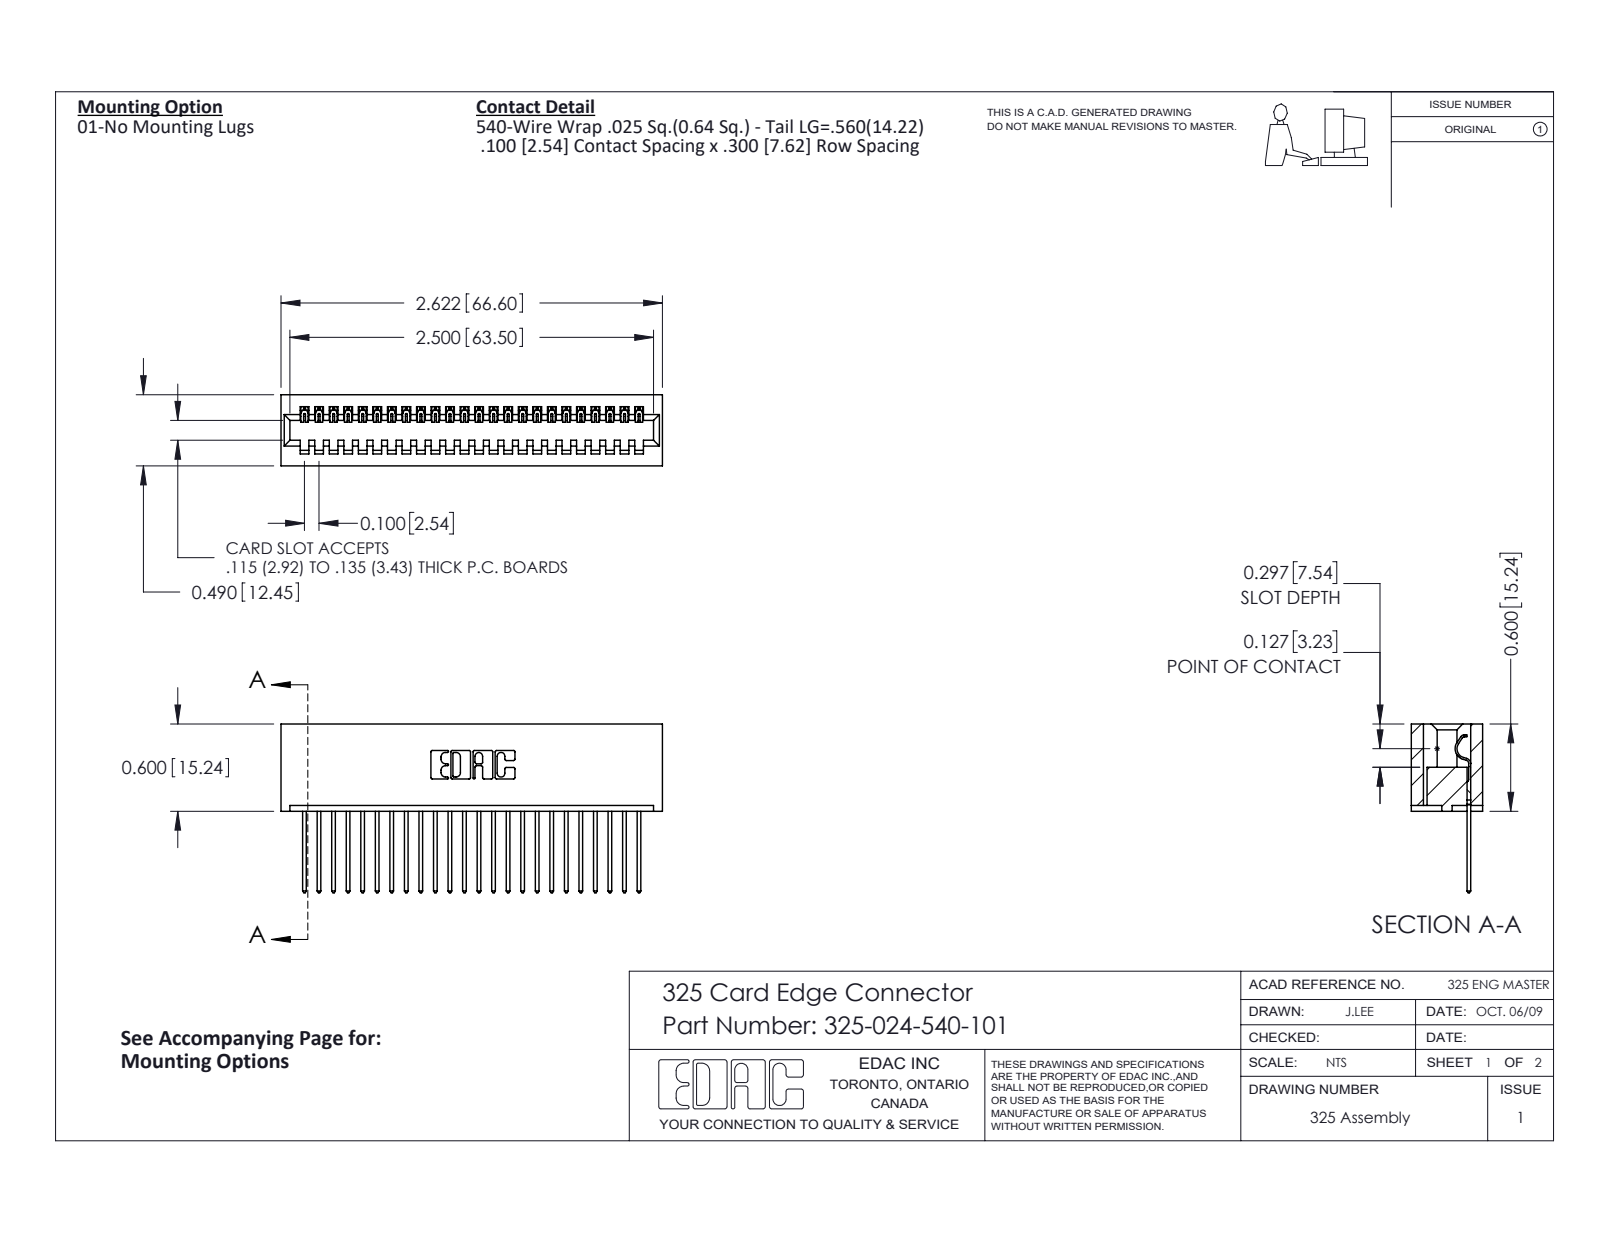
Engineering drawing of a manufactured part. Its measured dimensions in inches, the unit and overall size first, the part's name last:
Units: inches
Overall size (bounding box): 2.622 × 1.16 × 0.49
Partial cylindrical surfaces — rounded edges, fillets, slot ends (radius × count): R0.006 ×48, R0.01 ×48, R0.01 ×22, R0.007 ×6, R0.031 ×6, R0.026 ×3, R0.014 ×1, R0.022 ×1
Main face-to-face distances: 0.083, 0.407, 0.3, 0.49, 0.107, 0.383, 0.025, 0.56, 0.1, 0.325
Volume: 0.544 in³ · Surface area: 15.76 in²
Bodies: 25 solids, 1498 faces (1074 planar, 424 cylindrical, 0 other)
Part name (STEP PRODUCT): 325-024-540-101; 325 Part_Lugless; 325-292-001_325-293-140
STEP written by: SolidWorks 2016 (CONFIG_CONTROL_DESIGN)
